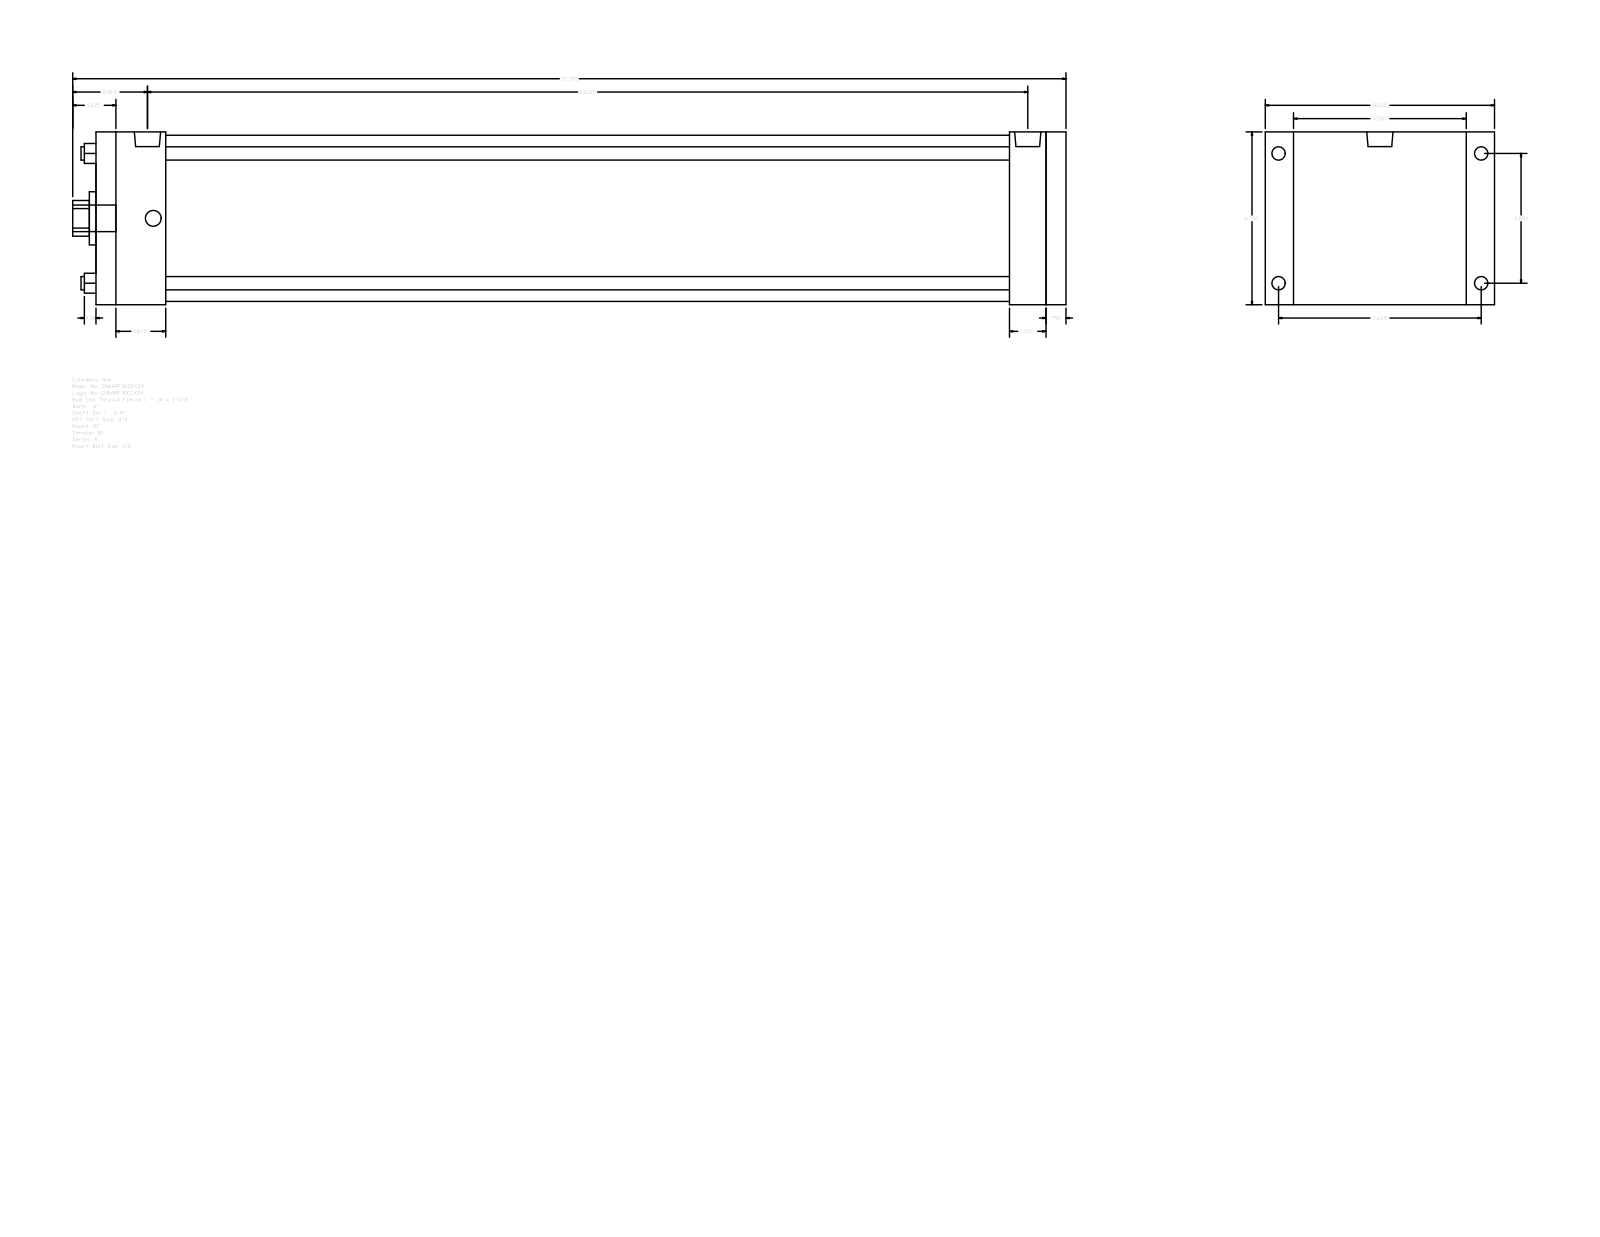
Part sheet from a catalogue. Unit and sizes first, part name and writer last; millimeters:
Units: millimetres
Overall size (bounding box): 949.33 × 219.07 × 165.1
Round holes (diameter × count): ⌀12.7 ×4, ⌀34.92 ×1, ⌀50.8 ×1, ⌀158.75 ×1
Round bosses / shafts (diameter × count): ⌀15.08 ×4, ⌀12.7 ×4, ⌀25.12 ×2, ⌀25.4 ×1
Partial cylindrical surfaces — rounded edges, fillets, slot ends (radius × count): R17.06 ×1
Main face-to-face distances: 165.1, 927.1, 908.04, 19.06, 66.67, 841.37, 860.43, 873.12, 806.45, 34.92
Hole centre spacings: 87.65, 123.96, 175.31
Bodies: 0 solids, 92 faces (64 planar, 28 cylindrical, 0 other)
Part name (STEP PRODUCT): A_RF__0600_1.375
STEP written by: GSSL Pune (CONFIG_CONTROL_DESIGN)
